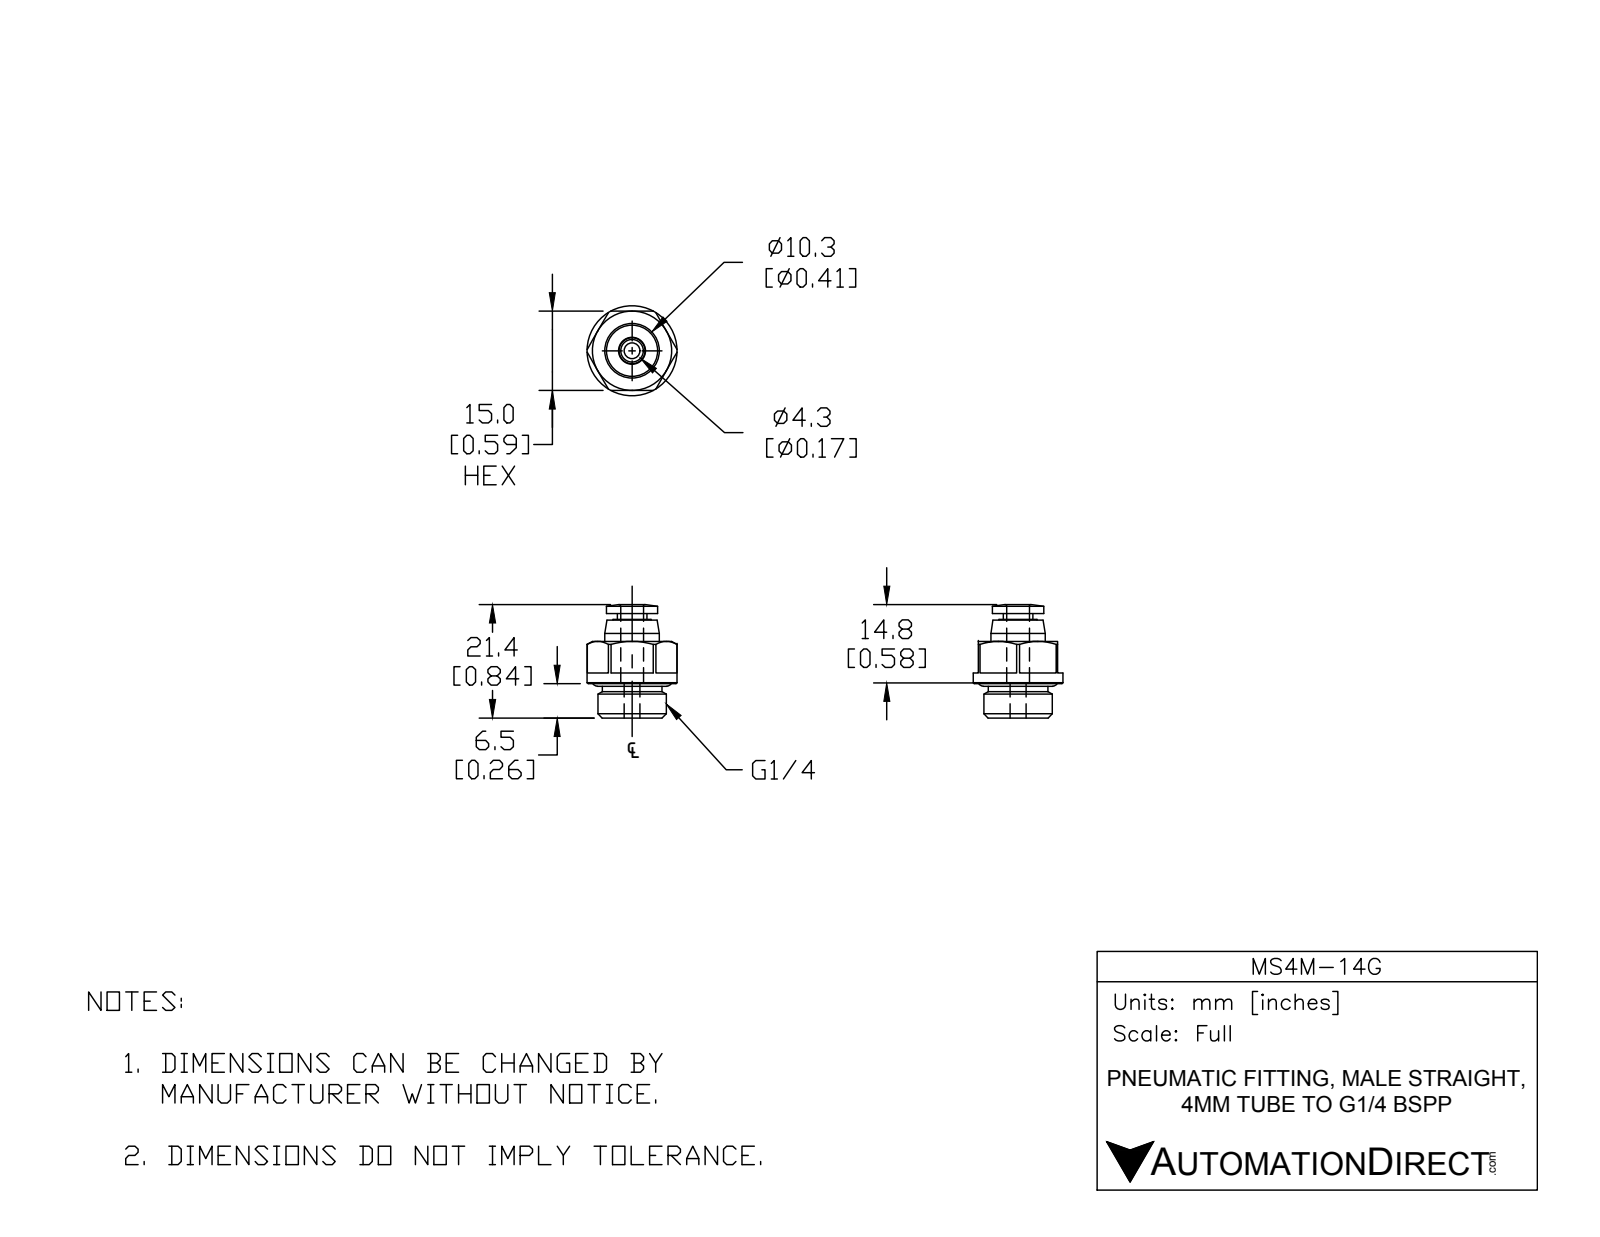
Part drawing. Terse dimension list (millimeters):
name: MS4M-14G
written by: SolidWorks 2018 (AUTOMOTIVE_DESIGN)
unit: mm
bodies: 2 solids, 64 faces (21 planar, 18 cylindrical, 25 other)
size: 21.4 × 17 × 17
volume: 2 640 mm³; area: 1 983 mm²
holes: 1× ⌀3, 1× ⌀4.3
bosses: 1× ⌀17, 1× ⌀13, 1× ⌀11.3, 1× ⌀10.3, 1× ⌀9.7, 1× ⌀7.2, 1× ⌀5.6
face distances: 15, 14.5, 19.8, 5.3, 1.2, 8.5, 6, 11.3, 11.9, 18.5
